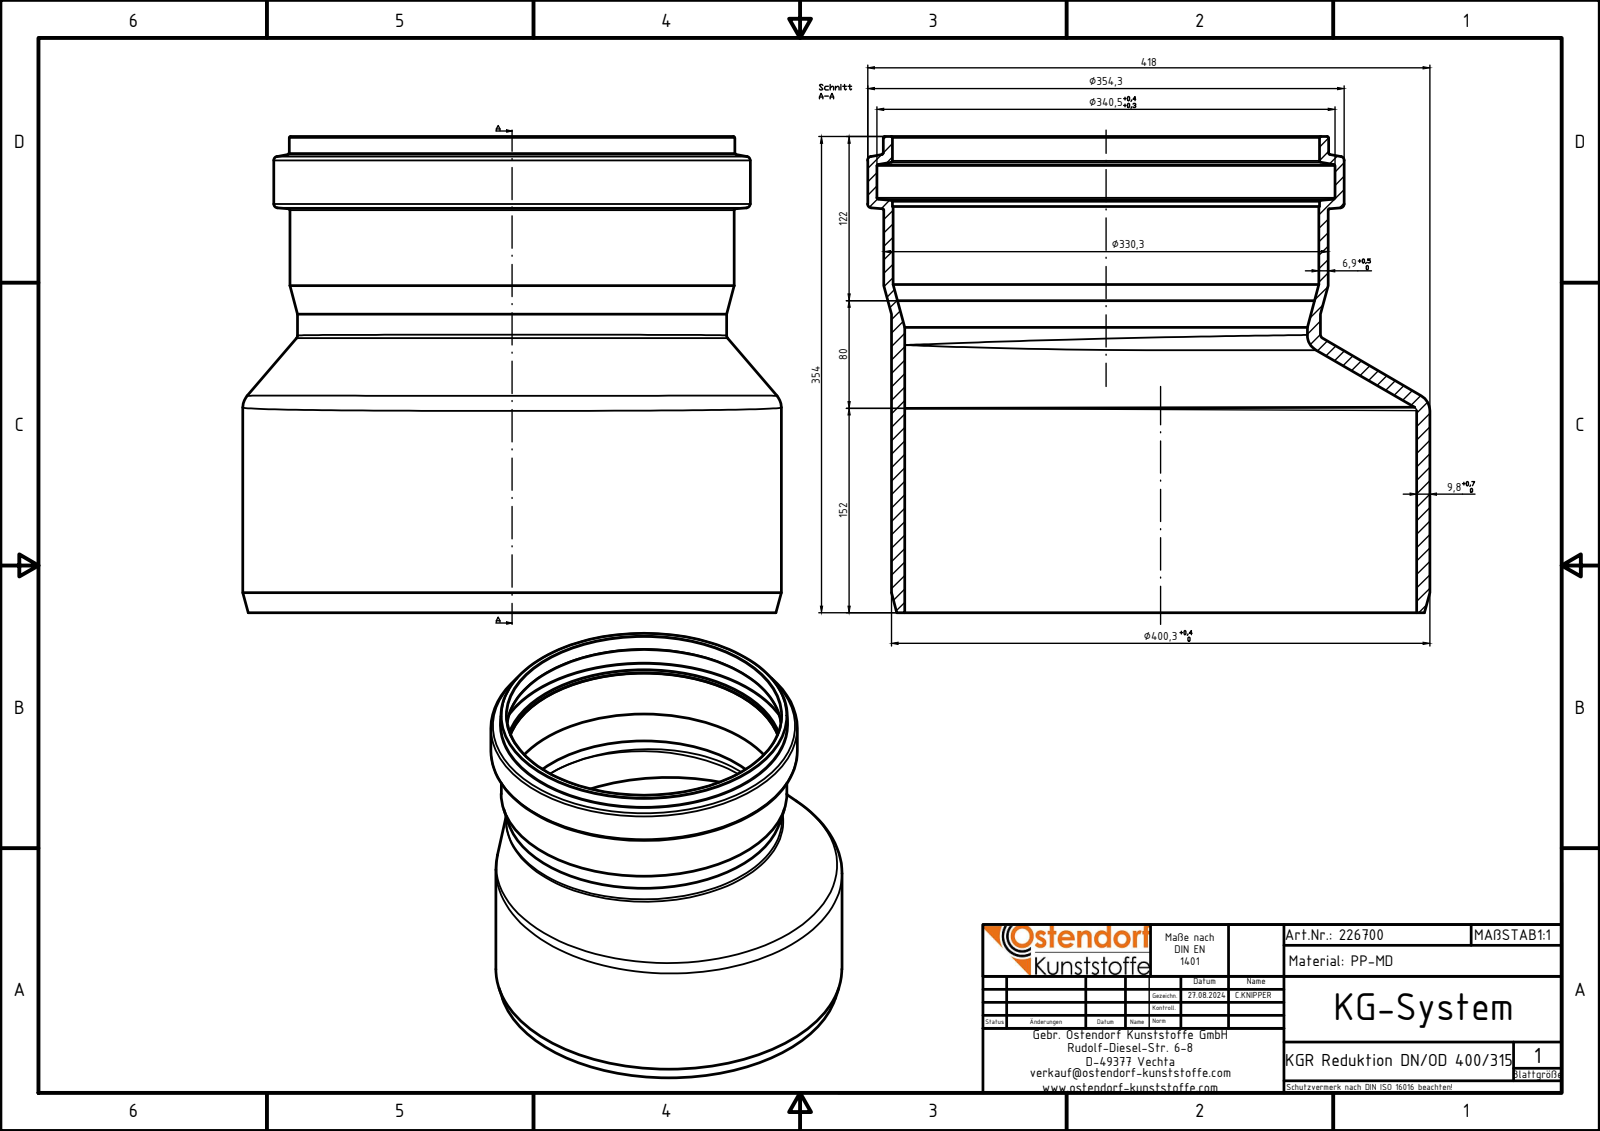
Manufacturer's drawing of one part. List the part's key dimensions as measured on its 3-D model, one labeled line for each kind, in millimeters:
Part name (STEP PRODUCT): 226700z
STEP written by: Autodesk Inventor 2024 (AUTOMOTIVE_DESIGN)
Units: millimetres
Bodies: 1 solid, 36 faces (3 planar, 11 cylindrical, 22 other)
Overall size (bounding box): 417.95 × 400.3 × 354
Volume: 3 850 000 mm³ · Surface area: 890 853 mm²
Round holes (diameter × count): ⌀299.4 ×1, ⌀316.5 ×1, ⌀317.4 ×1, ⌀340.5 ×1, ⌀380.7 ×1
Round bosses / shafts (diameter × count): ⌀400.3 ×1, ⌀354.3 ×1, ⌀331.2 ×1, ⌀330.3 ×1, ⌀319 ×1
Main face-to-face distances: 354, 302, 52
Hole centre spacings: 40.65
